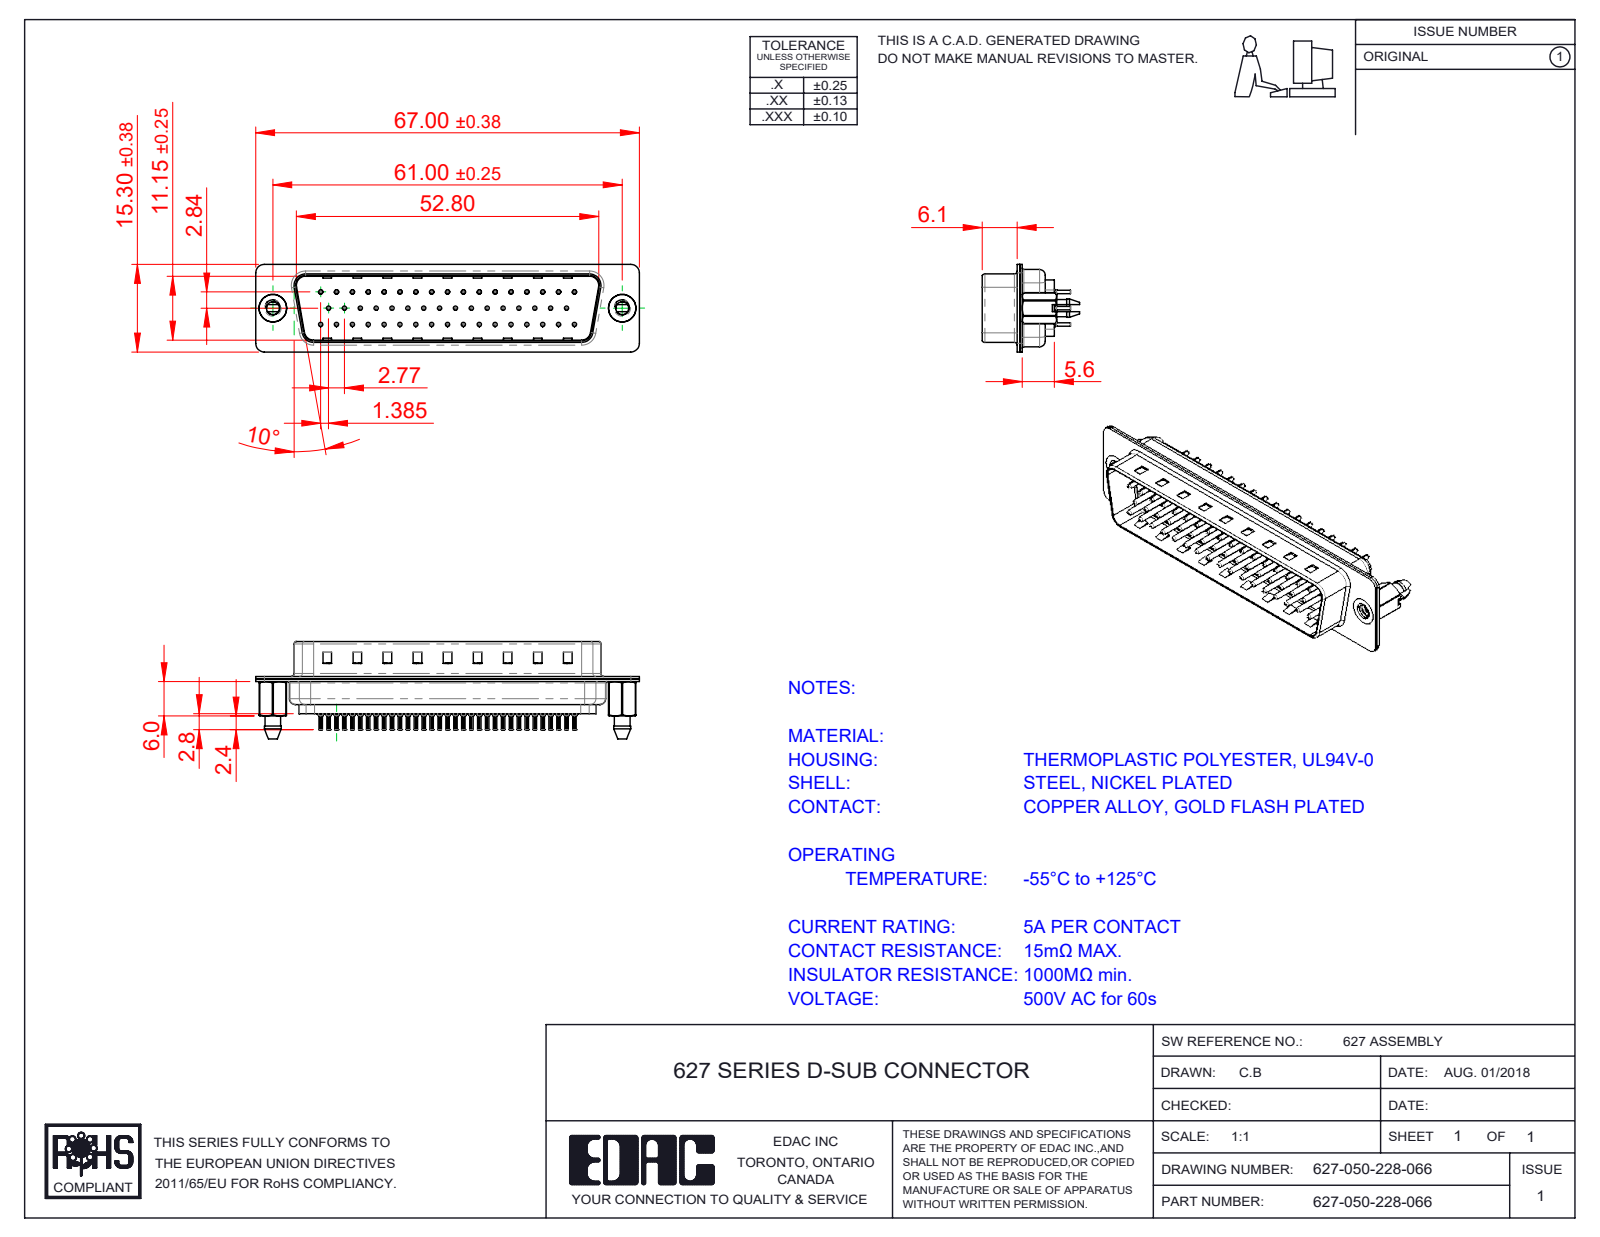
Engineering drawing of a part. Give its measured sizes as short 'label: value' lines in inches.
name: 627 Contact Row 1_28L; 627 Shell Front_50 Contacts; 627 Shell Rear_50 Contacts; 627 Contact Row 3_28L (+4 more)
written by: SolidWorks 2020 (CONFIG_CONTROL_DESIGN)
unit: in
bodies: 56 solids, 5579 faces (1441 planar, 2162 cylindrical, 1976 other)
size: 2.638 × 0.764 × 0.602
volume: 0.35 in³; area: 23.4 in²
holes: 50× ⌀0.008, 50× ⌀0.014, 50× ⌀0.043, 50× ⌀0.063, 2× ⌀0.089, 2× ⌀0.157, 2× ⌀0.189
bosses: 50× ⌀0.079, 50× ⌀0.059, 50× ⌀0.03, 50× ⌀0.024, 2× ⌀0.193
rounds: 100× R0.004, 18× R0.059, 12× R0.079, 10× R0.063, 8× R0.02, 4× R0.01, 4× R0.024, 4× R0.026
face distances: 0.016, 0.238, 0.018, 0.455, 0.035, 0.11, 0.348, 0.256, 0.366, 0.031
hole spacings: 0.109, 0.124, 0.218, 0.327, 0.436, 0.545, 0.654, 0.763
